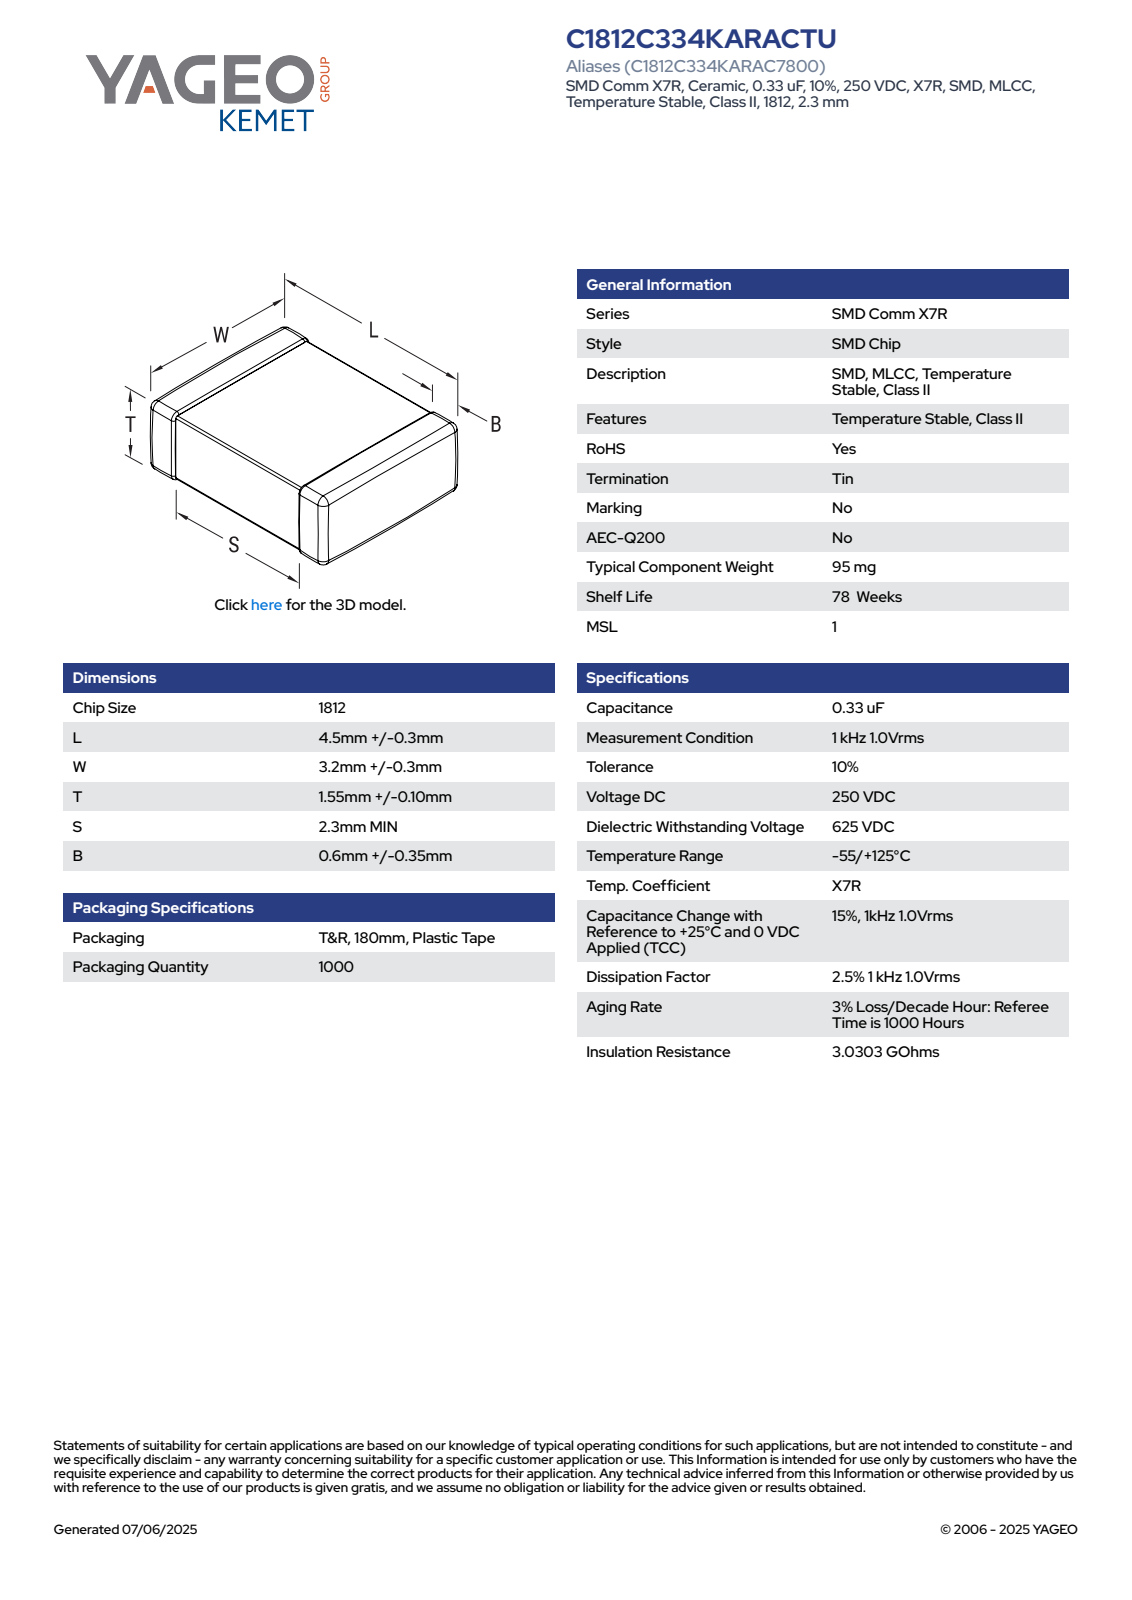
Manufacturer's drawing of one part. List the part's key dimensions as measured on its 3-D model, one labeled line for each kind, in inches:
Part name (STEP PRODUCT): CCS_CCSTDNOS_1812_L4.8W3.5T1.65B0.95
STEP written by: SolidWorks 2014 (AUTOMOTIVE_DESIGN)
Units: inches
Bodies: 4 solids, 125 faces (71 planar, 38 cylindrical, 16 other)
Overall size (bounding box): 0.189 × 0.138 × 0.065
Volume: 0.002 in³ · Surface area: 0.093 in²
Main face-to-face distances: 0.062, 0.059, 0.065, 0.189, 0.135, 0.132, 0.138, 0.059, 0.013, 0.076
